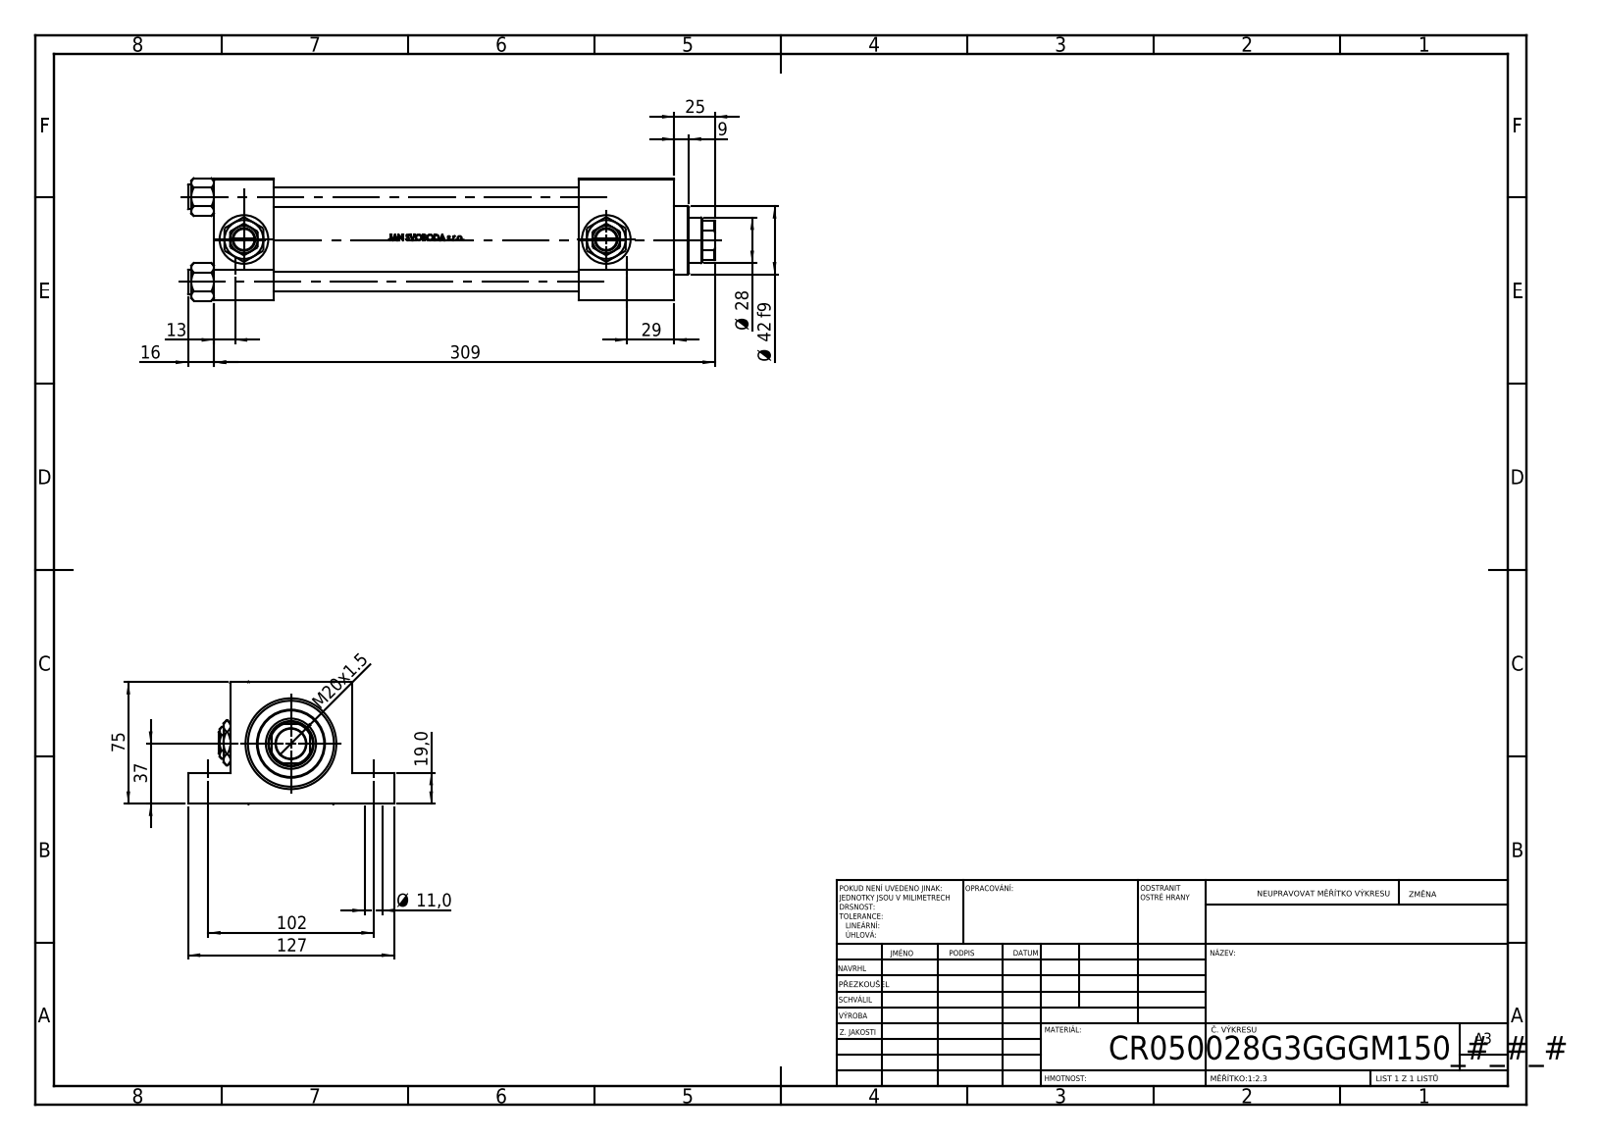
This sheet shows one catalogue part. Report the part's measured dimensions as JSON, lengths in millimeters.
{"part_name": "V215CR_VCP_G; NUT_M5_G; Zatka_pro_OIL_PORT; V215CR_G_TYCINKA (+2 more)", "step_written_by": "SolidWorks 2019 (CONFIG_CONTROL_DESIGN)", "units": "millimeters", "bodies": {"solids": 13, "faces": 1186, "planar": 478, "cylindrical": 134, "other": 574}, "overall_size": [325, 127, 75.54], "volume_mm3": 966087, "surface_area_mm2": 241921, "round_holes": [[11, 4], [12, 4], [20.96, 4], [30, 4], [7, 3], [18.5, 1], [28, 1], [31, 1], [41, 1], [50, 1], [53, 1]], "round_bosses_or_shafts": [[15, 4], [56, 1], [42, 1]], "partial_cylinders_radius": [[13.5, 1]], "face_to_face_distances": [75, 37, 284, 247, 19, 56, 225, 188, 59, 26], "hole_center_spacings": [52.3, 36.63, 37.34, 51.3, 52.63, 73.96, 102, 223.5]}
